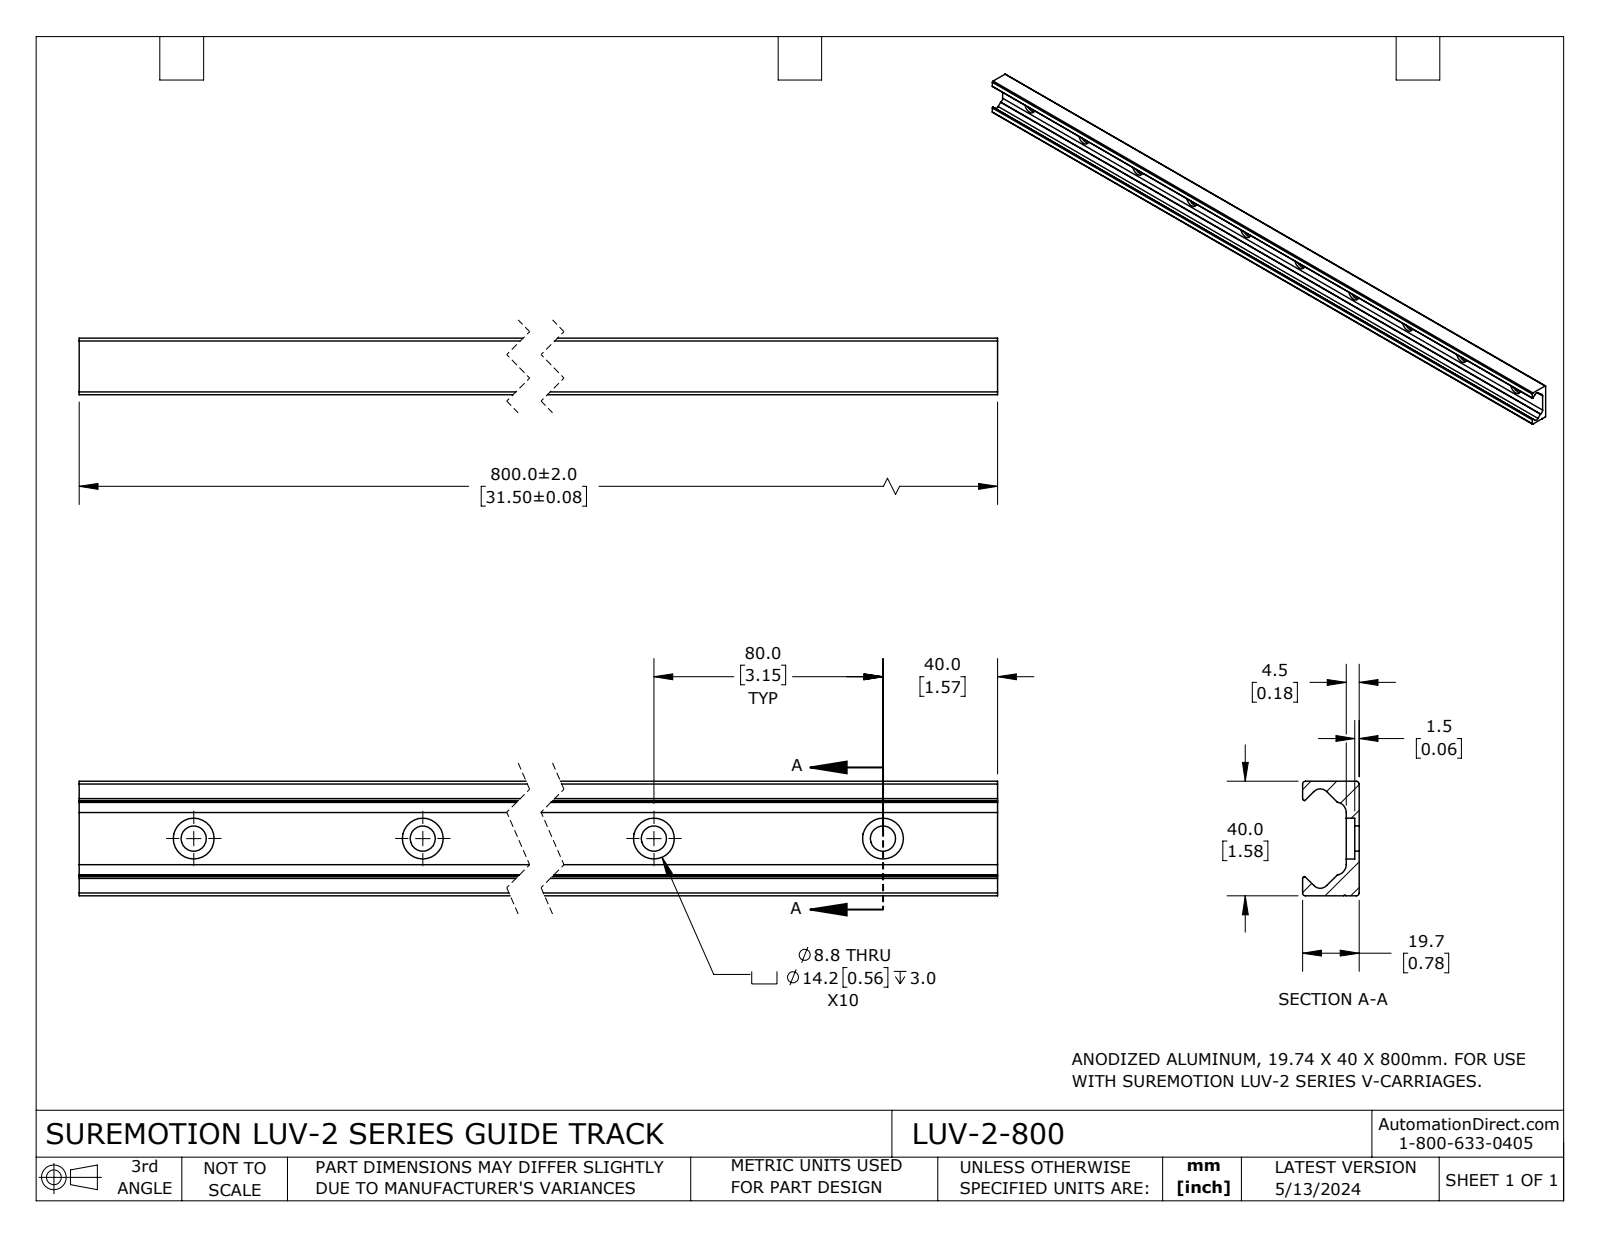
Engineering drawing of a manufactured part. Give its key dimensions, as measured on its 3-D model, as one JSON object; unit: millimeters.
{"part_name": "LUV-2-800", "step_written_by": "SolidWorks 2023 (CONFIG_CONTROL_DESIGN)", "units": "millimeters", "bodies": {"solids": 1, "faces": 78, "planar": 23, "cylindrical": 55, "other": 0}, "overall_size": [800, 40.01, 19.74], "volume_mm3": 266208, "surface_area_mm2": 121596, "round_holes": [[8.81, 10], [14.25, 10]], "partial_cylinders_radius": [[0.99, 4], [0.43, 2], [0.64, 2], [0.64, 2], [3.18, 2], [3.61, 2], [0.33, 1]], "face_to_face_distances": [40.02, 4.5, 19.74, 15.24, 26.37, 1.5, 3, 18.24, 800], "hole_center_spacings": [80, 160, 240, 320, 400, 480, 560, 640]}
